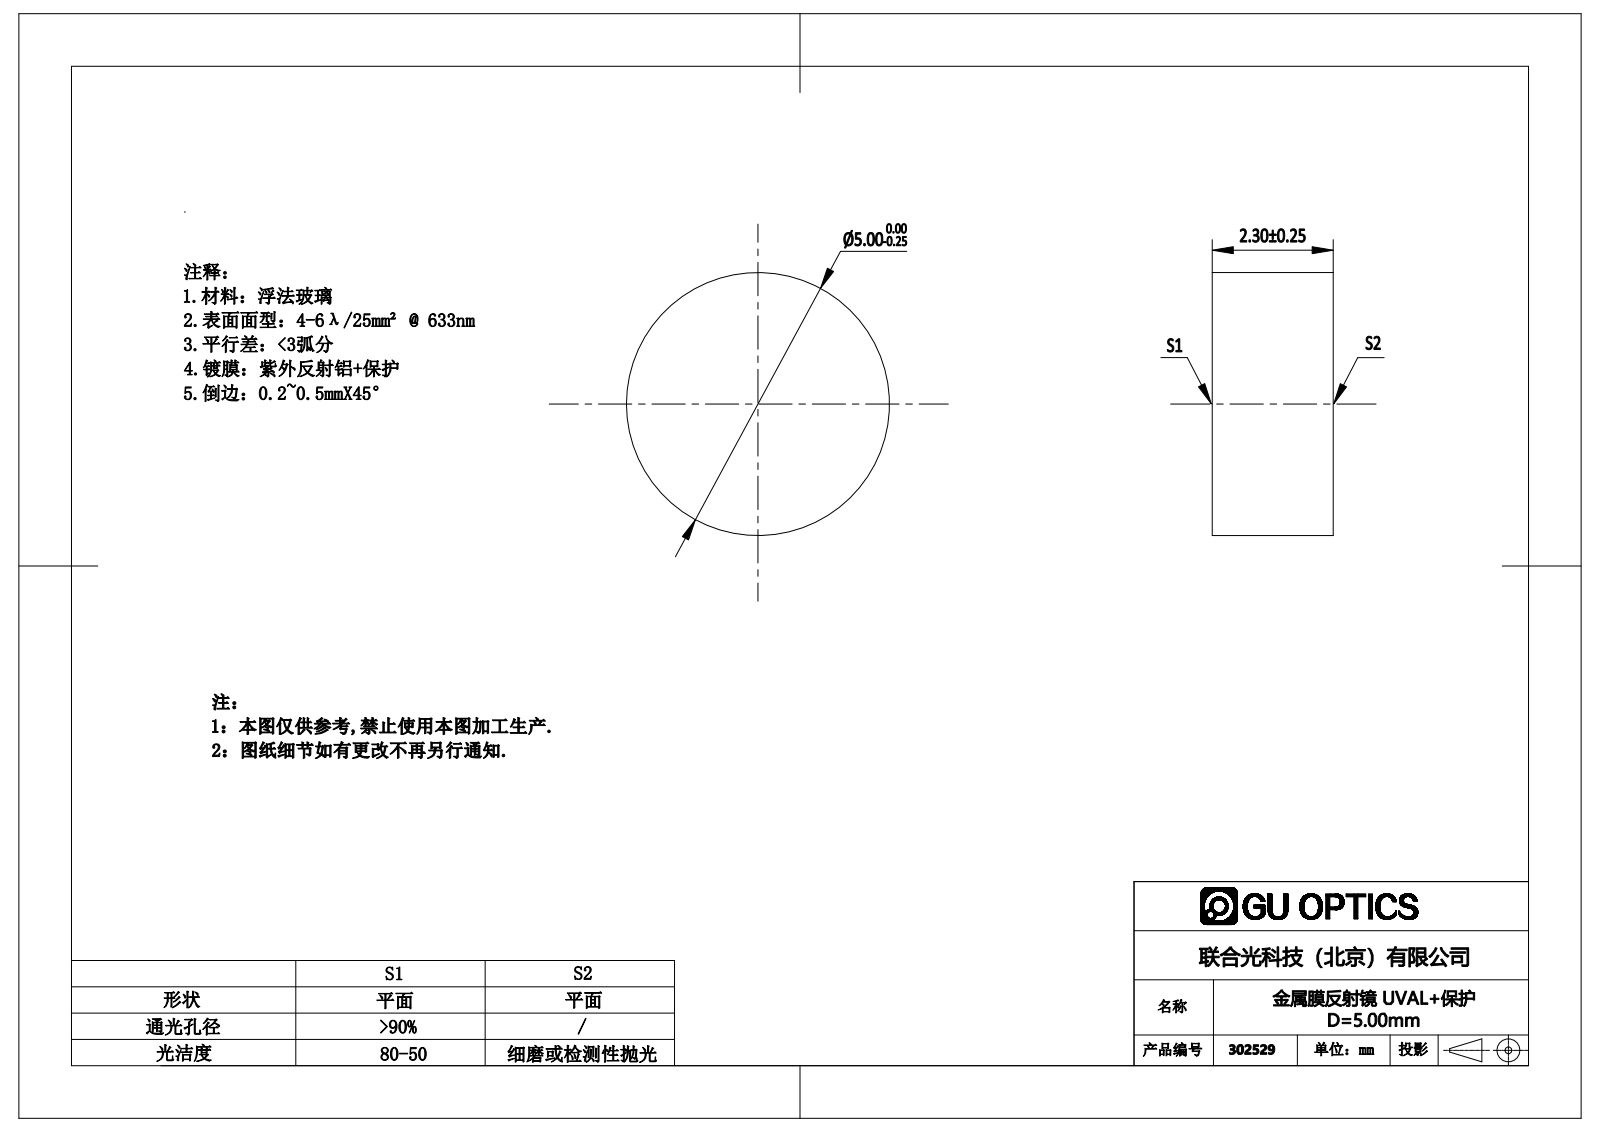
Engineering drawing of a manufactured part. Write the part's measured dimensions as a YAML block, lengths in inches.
part_name: "302500"
step_written_by: "SolidWorks 2016 (AUTOMOTIVE_DESIGN)"
units: inches
bodies: {solids: 1, faces: 4, planar: 2, cylindrical: 2, other: 0}
overall_size: [0.197, 0.197, 0.091]
volume: 0.003
surface_area: 0.12
round_bosses_or_shafts:
  - {diameter: 0.197, count: 1}
face_to_face_distances: [0.091]
